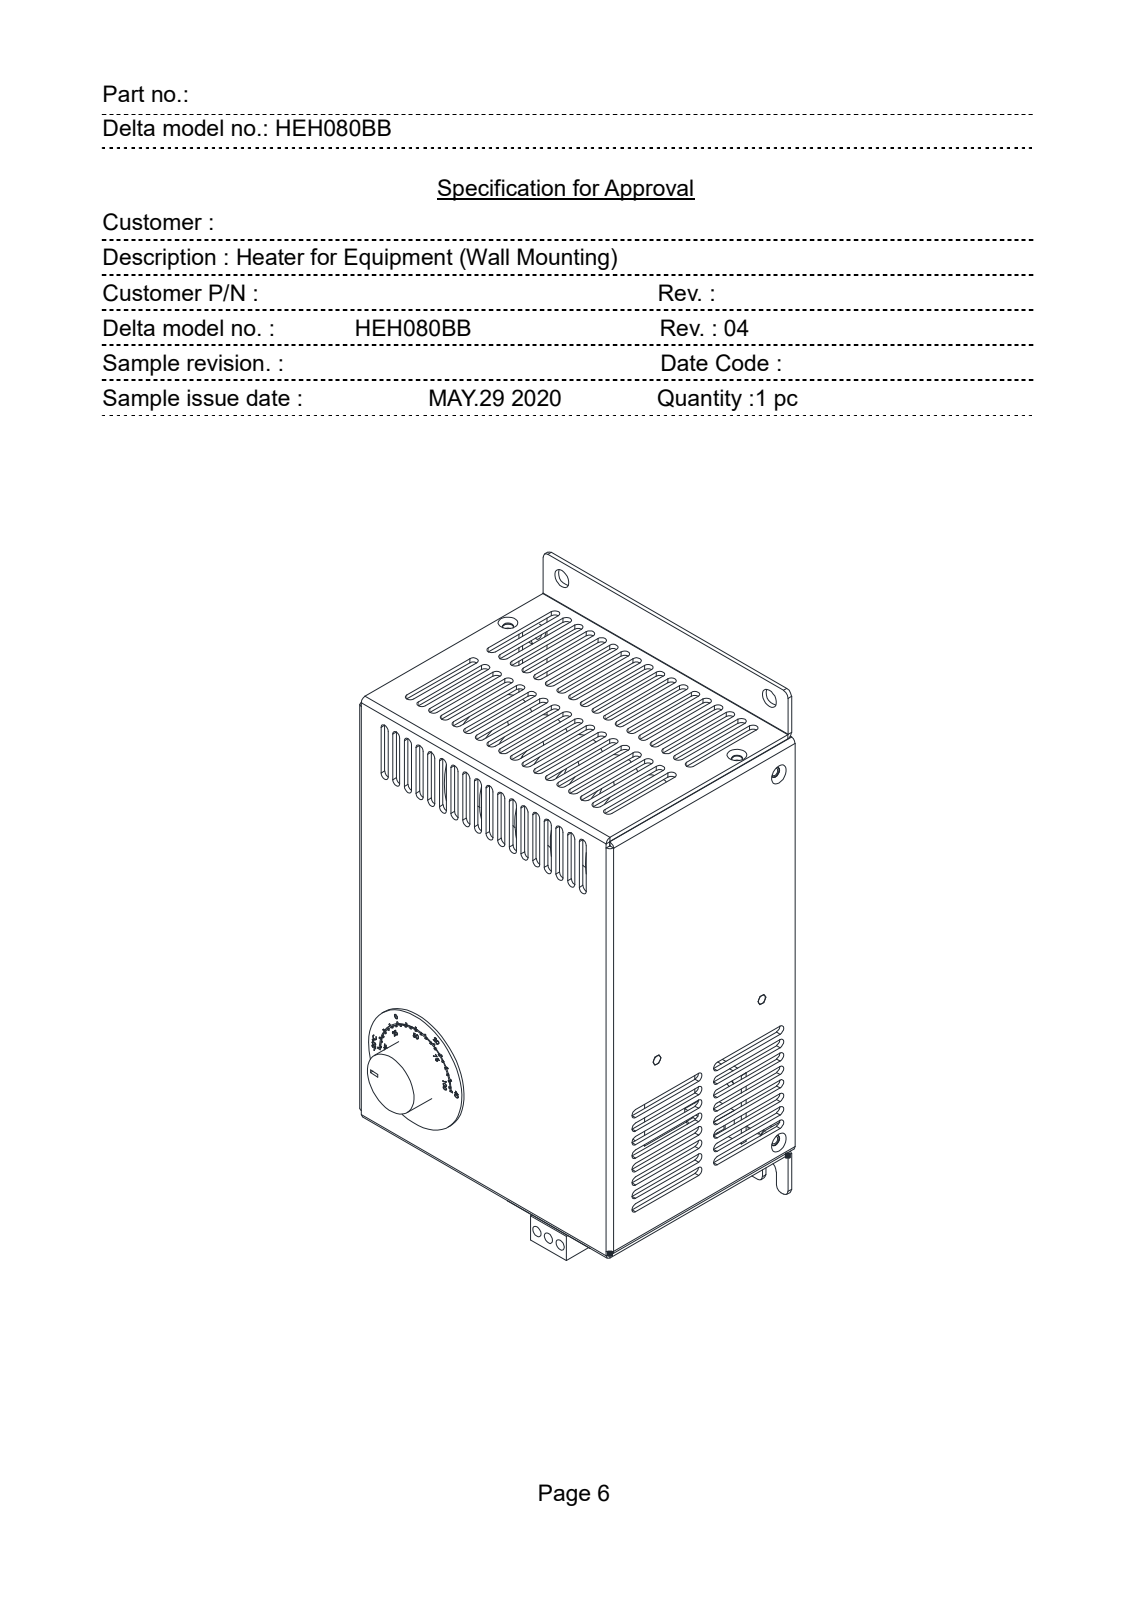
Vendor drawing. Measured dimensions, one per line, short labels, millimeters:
name: HEH080BB-AB_20205020
written by: SolidWorks 2016 (AUTOMOTIVE_DESIGN)
unit: mm
bodies: 0 solids, 1295 faces (659 planar, 453 cylindrical, 183 other)
size: 187.45 × 108.2 × 91
holes: 6× ⌀2.5, 6× ⌀3.5, 4× ⌀3.4, 3× ⌀3, 3× ⌀4.5, 2× ⌀3.64, 2× ⌀5.7, 2× ⌀6, 1× ⌀40
bosses: 3× ⌀6.35, 2× ⌀4.2, 1× ⌀40, 1× ⌀20, 1× ⌀3.82, 1× ⌀3, 1× ⌀1.46, 1× ⌀1.19
rounds: 140× R1.5, 12× R2, 10× R1.6, 7× R0.1, 4× R0.3, 2× R1, 2× R1.51, 2× R3
face distances: 1.5, 78, 106.7, 76.5, 79.5, 105.2, 108.2, 154.7, 7.8, 68.7
hole spacings: 35.36, 5, 7.45, 23.91, 50, 0.5, 1.52, 6.96
